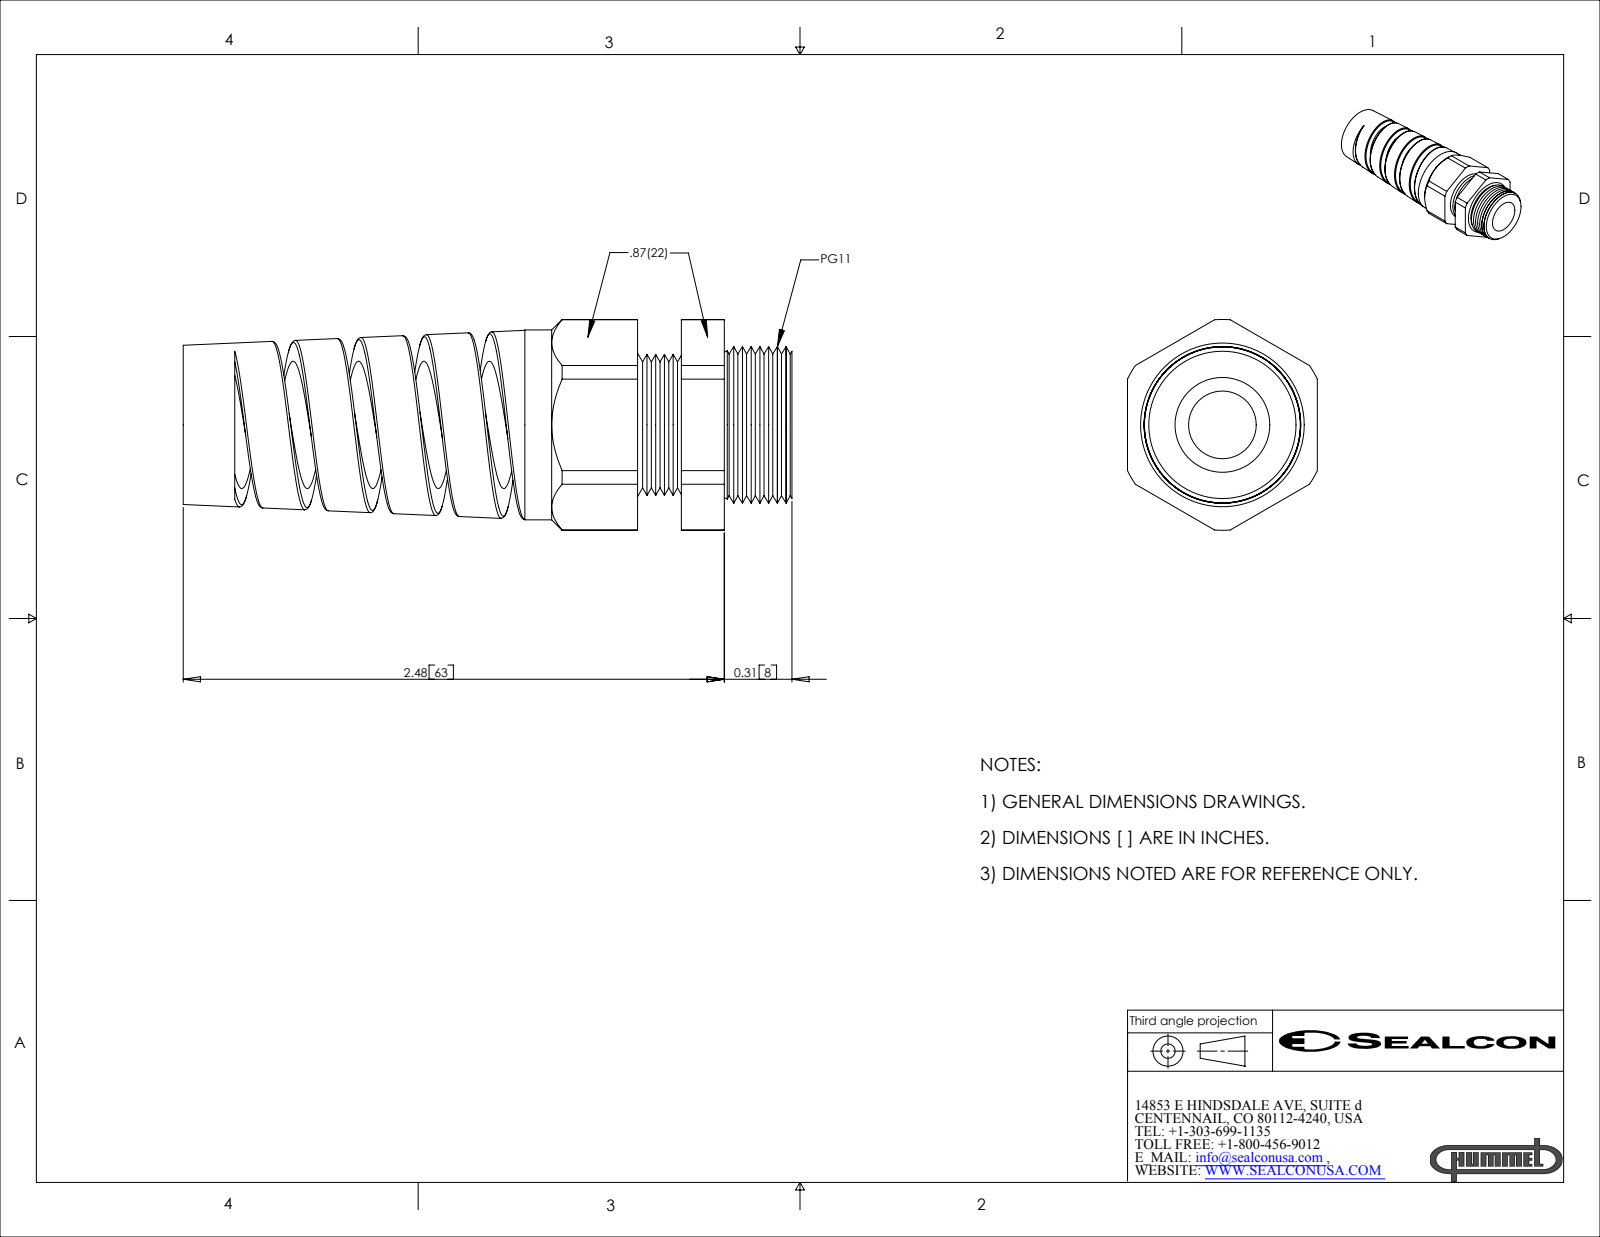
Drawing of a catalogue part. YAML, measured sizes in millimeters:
part_name: "CF11BA-GY"
step_written_by: "SolidWorks 2007 (CONFIG_CONTROL_DESIGN)"
units: millimeters
bodies: {solids: 2, faces: 146, planar: 24, cylindrical: 35, other: 87}
overall_size: [70.9, 24.5, 22.1]
volume: 12700
surface_area: 10610
round_holes:
  - {diameter: 7.9, count: 1}
  - {diameter: 14.8, count: 1}
  - {diameter: 16.7, count: 1}
round_bosses_or_shafts:
  - {diameter: 22.1, count: 1}
partial_cylinders:
  - {radius: 7.7, count: 1}
  - {radius: 12.3, count: 1}
face_to_face_distances: [22.1, 5.1, 10.1, 5, 18, 12.9, 7.9, 11.3, 16.3, 21.3]
